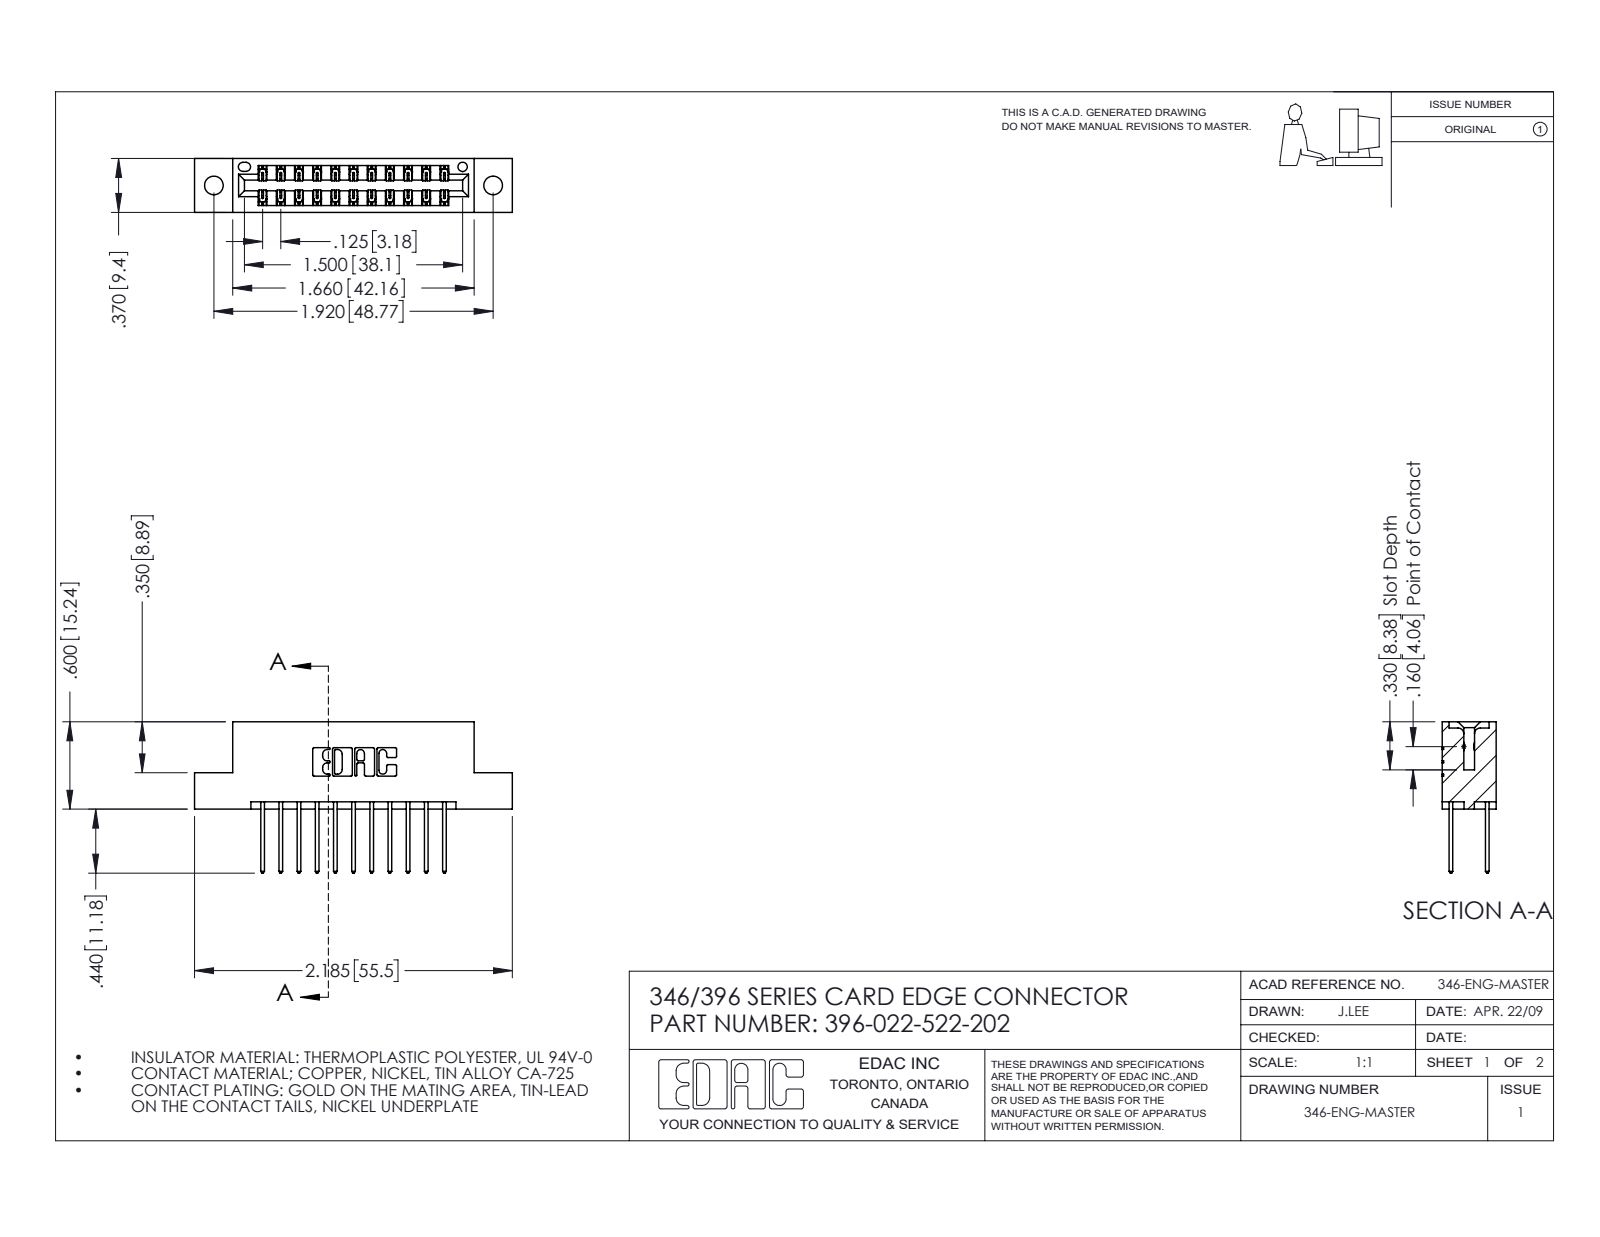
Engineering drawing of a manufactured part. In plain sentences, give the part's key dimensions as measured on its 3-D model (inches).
The part is named "396-022-522-202; 345-292-001_345-293-122; 346 Part_Flush Mounting Lugs - 0.128 Dia". Its 3-D file was written by "SolidWorks 2016 (CONFIG_CONTROL_DESIGN)". It is 23 solids with 1266 faces: 846 planar, 420 cylindrical and 0 other. Overall it measures 2.185 by 1.04 by 0.37 inches. Its volume is 0.317 cubic inches and its surface area 10.29 square inches. Round holes: 2 of diameter 0.128, 1 of diameter 0.064. Partial cylindrical surfaces (rounded edges, fillets, slot ends): 33 of radius 0.006, 22 of radius 0.01, 22 of radius 0.01, 6 of radius 0.007, 6 of radius 0.031, 3 of radius 0.026, 2 of radius 0.014, 2 of radius 0.022. The main face-to-face distances are 0.25, 0.048, 0.322, 0.37, 0.072, 0.298, 0.025, 0.275, 0.148, 0.222. The hole center spacings are 0.246, 1.715, 1.92.
